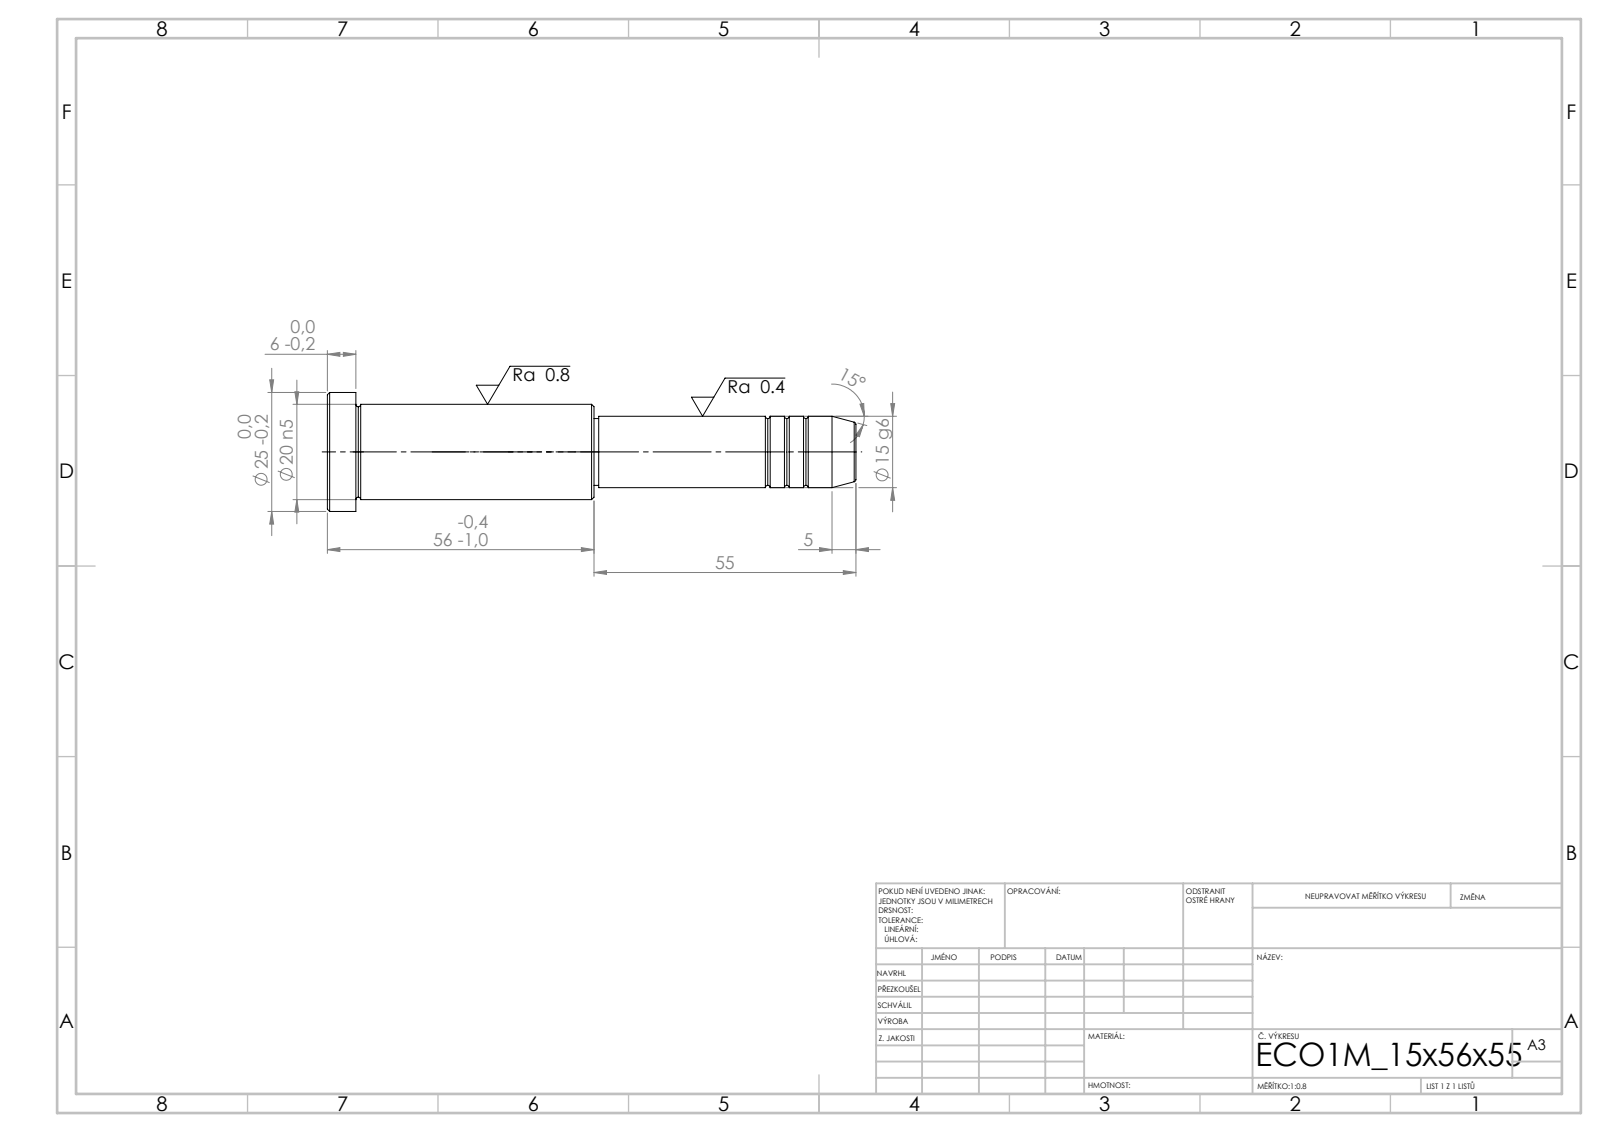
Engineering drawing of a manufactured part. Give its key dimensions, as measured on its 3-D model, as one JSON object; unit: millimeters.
{"step_written_by": "SolidWorks 2019 (CONFIG_CONTROL_DESIGN)", "units": "millimeters", "bodies": {"solids": 1, "faces": 43, "planar": 5, "cylindrical": 14, "other": 24}, "overall_size": [111, 25, 25], "volume_mm3": 28105, "surface_area_mm2": 7215, "round_bosses_or_shafts": [[25, 1], [20, 1], [15, 1], [14, 1]], "face_to_face_distances": [6, 50, 56, 55, 105, 111, 54, 1, 51, 57]}
